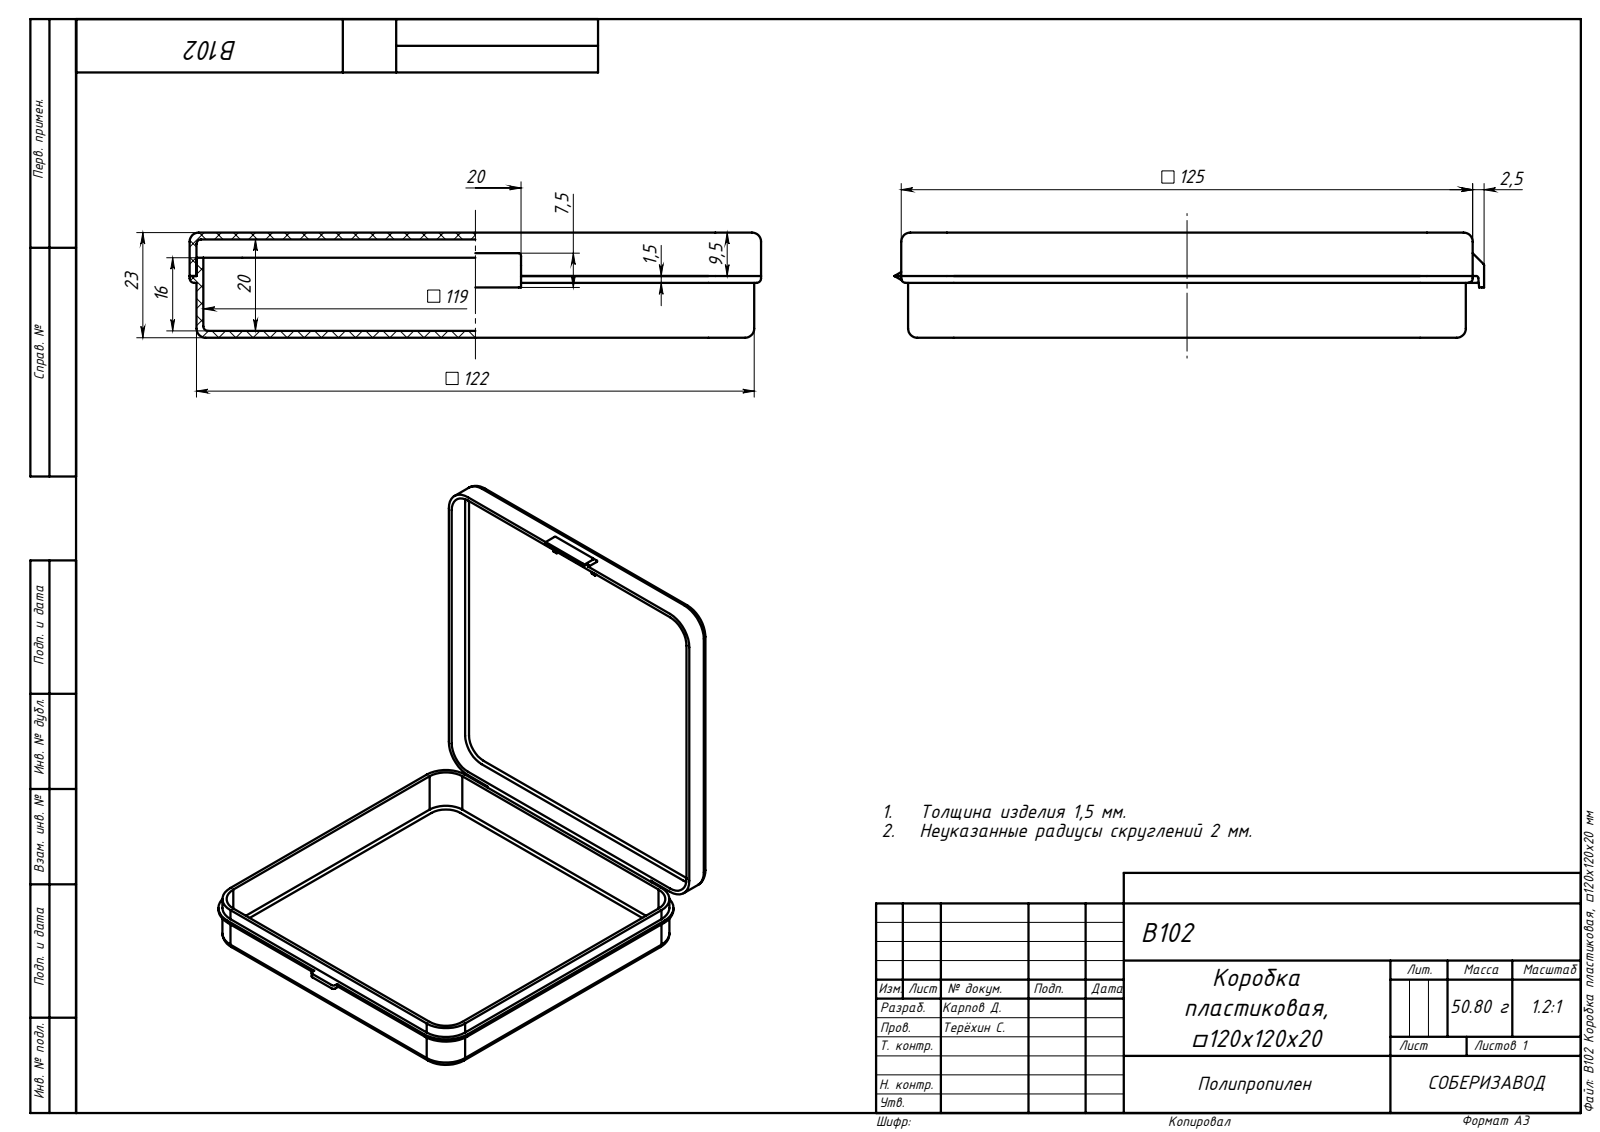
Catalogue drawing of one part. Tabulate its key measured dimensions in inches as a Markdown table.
| quantity | value |
| --- | --- |
| part name | B102 Емкость; B102 Коробка пластиковая, ?120x120x20 мм; B102 Крышка |
| STEP written by | SolidWorks 2020 (AUTOMOTIVE_DESIGN) |
| units | inches |
| bodies | 2 solids, 141 faces (61 planar, 58 cylindrical, 22 other) |
| overall size | 5.079 × 4.921 × 0.906 |
| volume | 3.858 in³ |
| surface area | 132.4 in² |
| partial cylindrical surfaces (radius × count) | 0.039 × 14, 0.02 × 8, 0.079 × 8, 0.335 × 8, 0.394 × 8, 0.453 × 4 |
| main face-to-face distances | 0.059, 0.846, 0.906, 0.787, 4.803, 4.744, 0.118, 4.862, 4.685, 0.472 |
